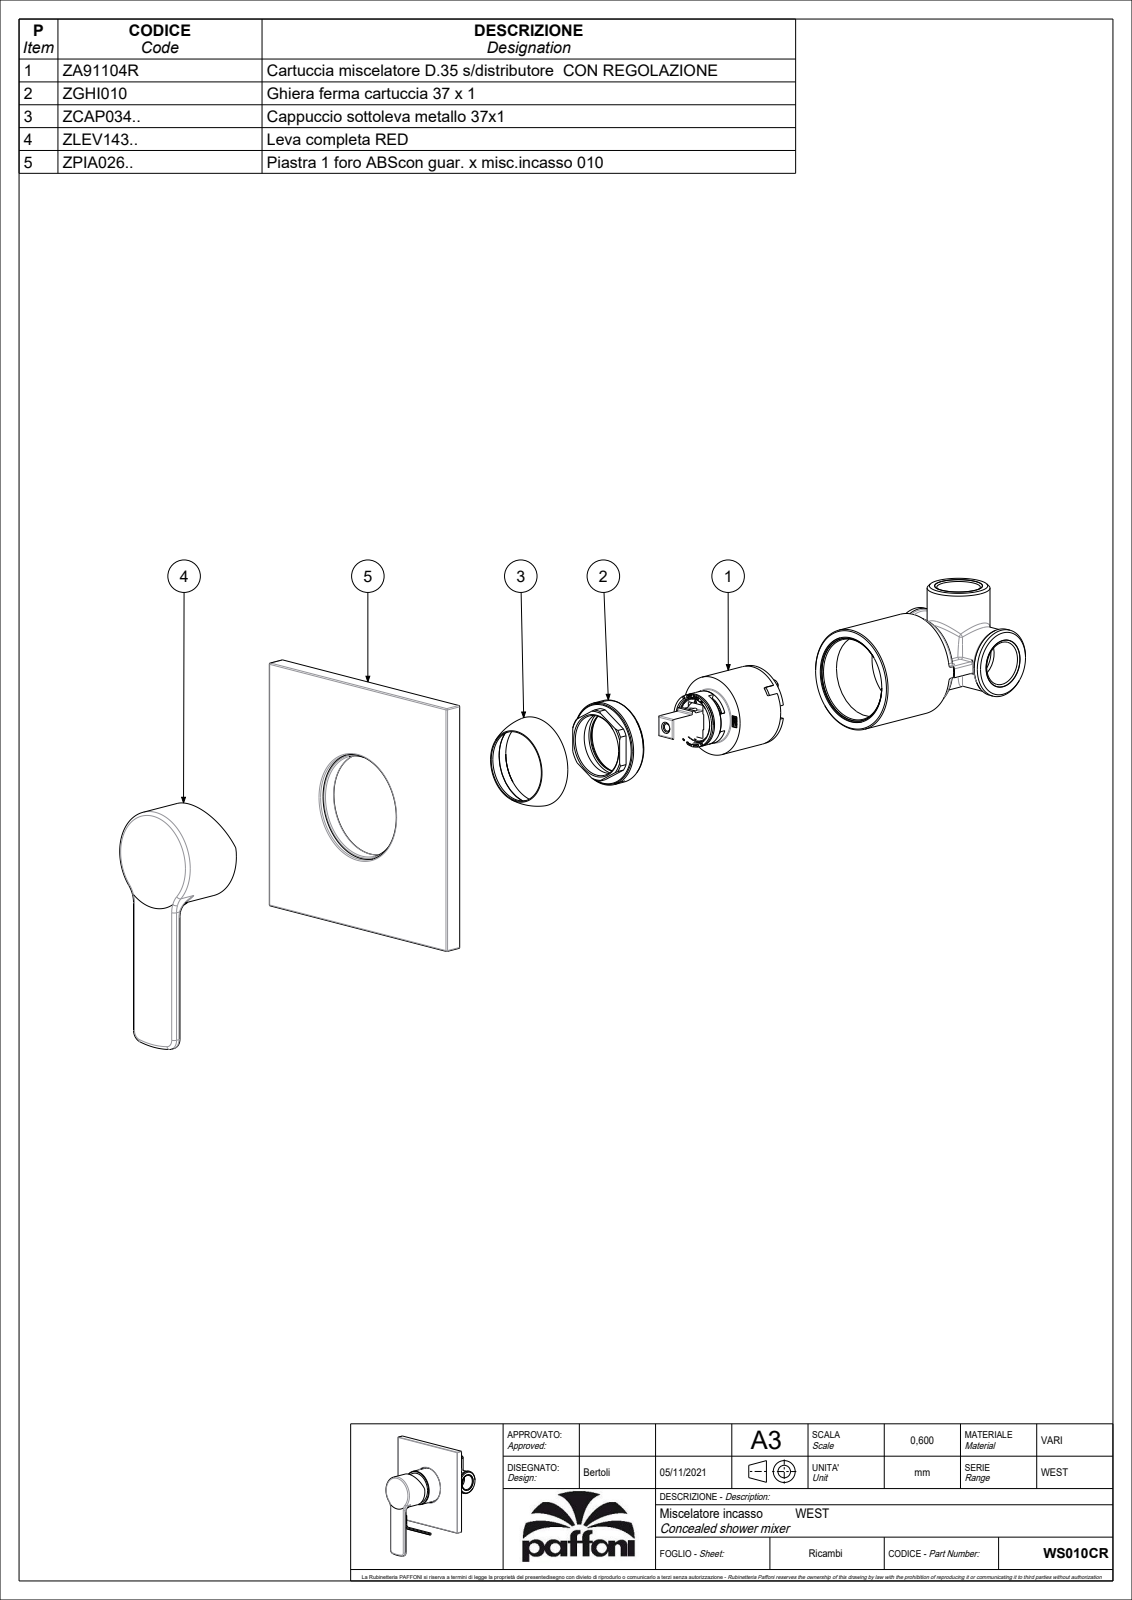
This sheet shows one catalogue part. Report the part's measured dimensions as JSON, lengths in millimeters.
{"part_name": "WS010CR", "step_written_by": "CREO PARAMETRIC BY PTC INC, 2020044 (CONFIG_CONTROL_DESIGN)", "units": "millimeters", "bodies": {"solids": 2, "faces": 1112, "planar": 611, "cylindrical": 289, "other": 212}, "overall_size": [140, 110, 64.83], "volume_mm3": 115331, "surface_area_mm2": 72941, "round_holes": [[3.3, 2], [4, 2], [3, 1], [4.5, 1], [5, 1], [19.5, 1], [19.9, 1], [26.8, 1], [29, 1], [31, 1], [32.4, 1], [36, 1]], "round_bosses_or_shafts": [[51, 1], [44.8, 1], [43, 1], [35, 1], [32.2, 1], [23.5, 1], [23.4, 1], [21.8, 1]], "partial_cylinders_radius": [[0.5, 82], [0.15, 11], [1, 6], [0.3, 4], [1.5, 4], [2, 4], [5, 2], [10, 2]], "face_to_face_distances": [7, 2, 1, 8, 6, 2.5, 5, 0.5, 108, 59.1], "hole_center_spacings": [12.5]}
